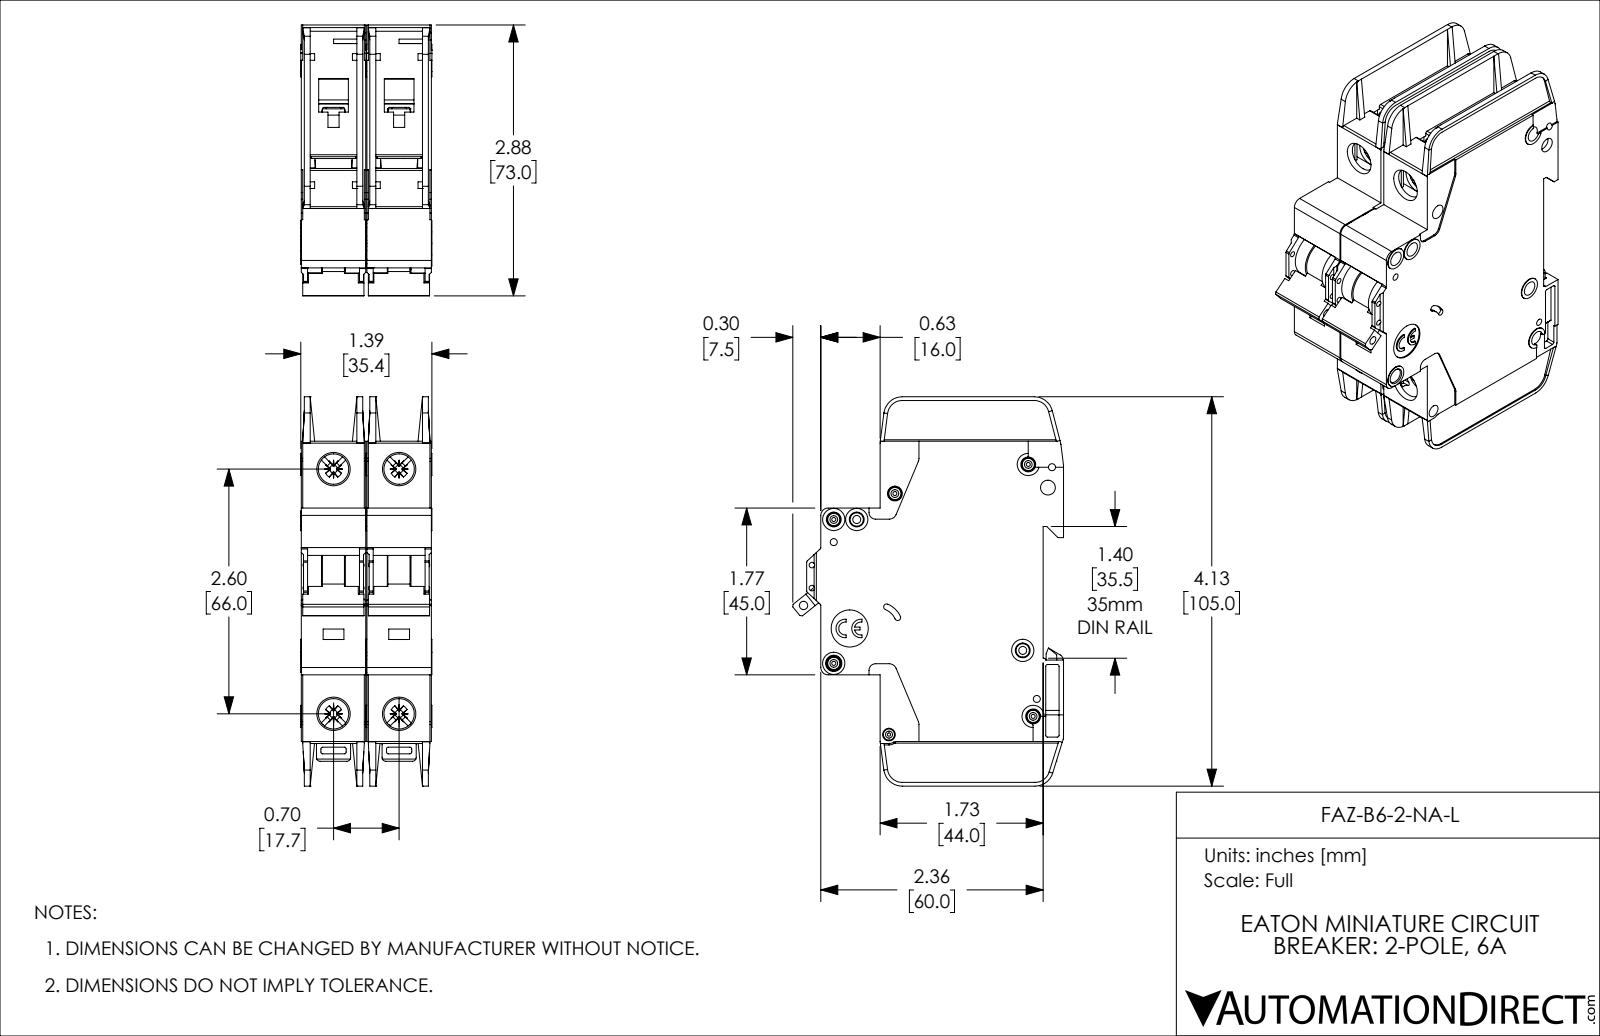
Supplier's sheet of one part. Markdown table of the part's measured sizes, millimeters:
| quantity | value |
| --- | --- |
| part name | FAZ-B6-2-NA-L |
| STEP written by | SolidWorks 2019 (AUTOMOTIVE_DESIGN) |
| units | millimeters |
| bodies | 2 solids, 2254 faces (1342 planar, 714 cylindrical, 198 other) |
| overall size | 105 × 73.1 × 35.4 |
| volume | 153 500 mm³ |
| surface area | 52 910 mm² |
| round holes (diameter × count) | 4 × 8, 1.1 × 5, 1.9 × 4, 8.2 × 4, 1.5 × 2, 2.2 × 2, 0.9 × 1, 2.3 × 1, 2.5 × 1, 3.4 × 1, 10 × 1 |
| round bosses / shafts (diameter × count) | 3.3 × 5, 6 × 4, 3 × 3, 2.5 × 2 |
| partial cylindrical surfaces (radius × count) | 0.5 × 57, 0.4 × 20, 1 × 14, 2 × 10, 1.1 × 8, 0.2 × 5, 5 × 5, 0.3 × 4 |
| main face-to-face distances | 17.7, 1.2, 17.4, 15, 2.4, 16.2, 13.8, 35.1, 18.9, 16.5 |
| hole center spacings | 6.2, 13.6, 17.7, 22.1, 66, 68.3, 4.8, 5.1 |
